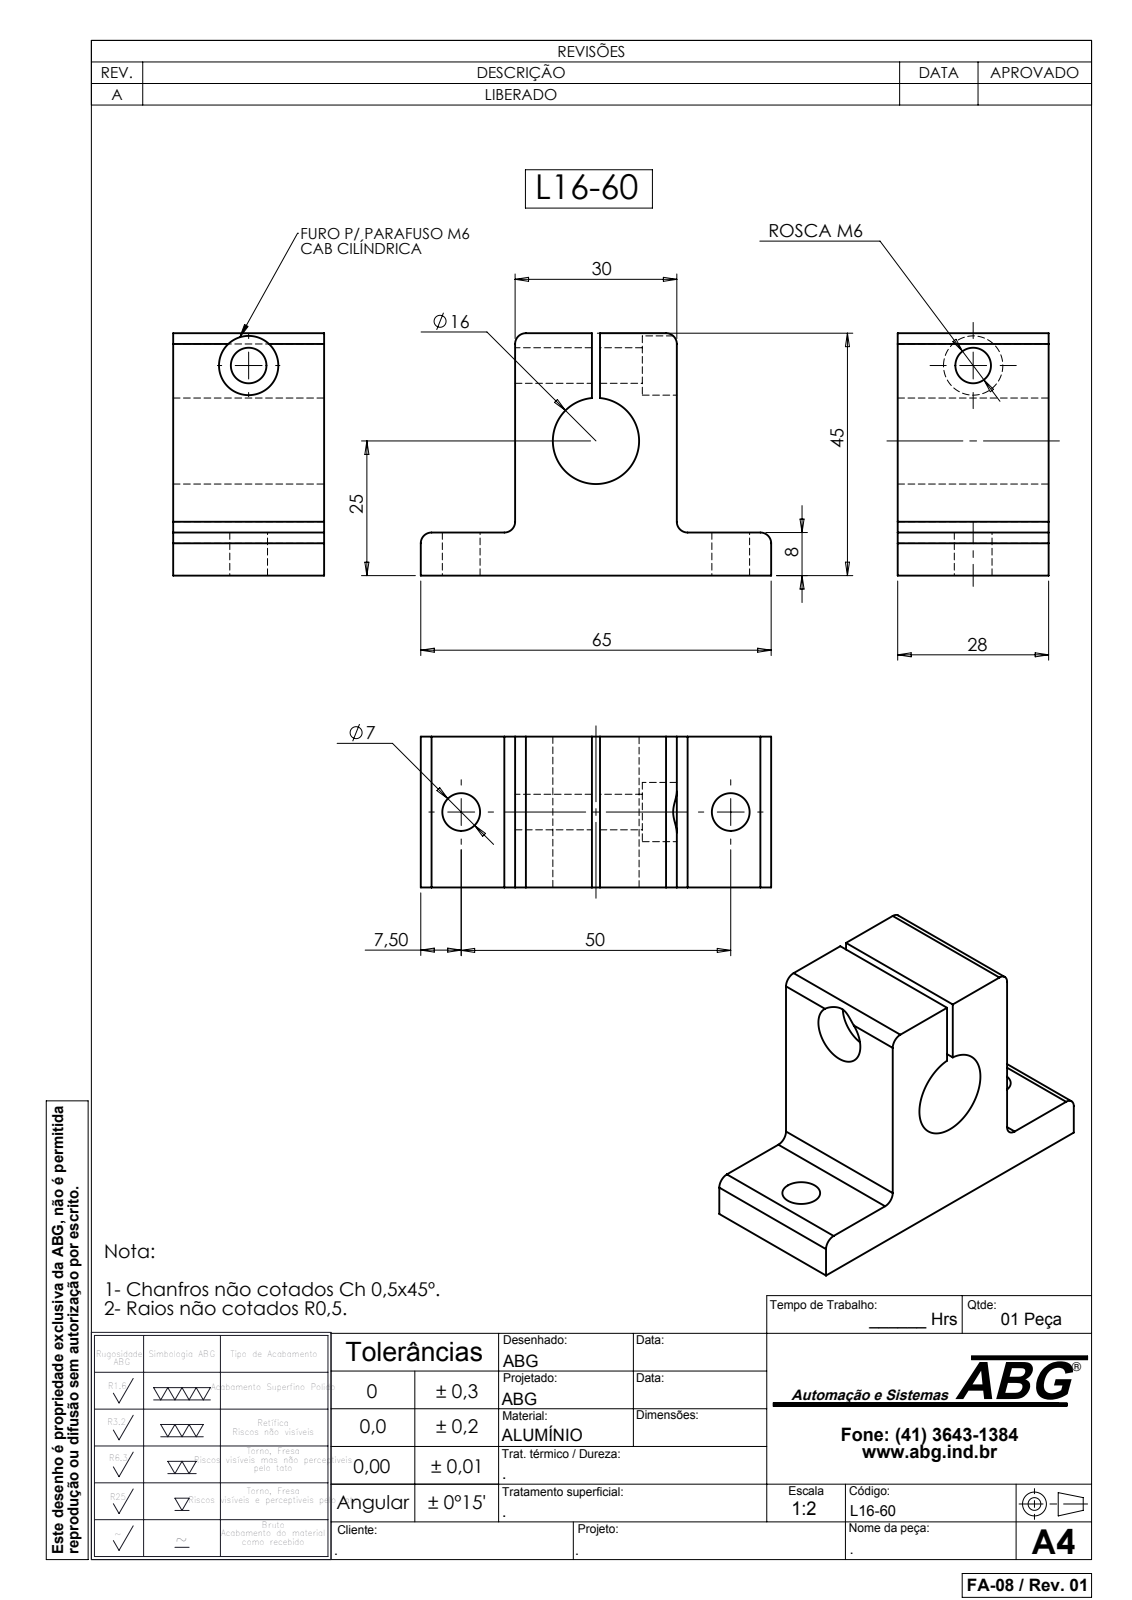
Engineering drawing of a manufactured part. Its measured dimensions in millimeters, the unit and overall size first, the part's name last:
Units: millimetres
Overall size (bounding box): 65 × 45 × 28
Round holes (diameter × count): ⌀7 ×2, ⌀6.6 ×1, ⌀11 ×1, ⌀16 ×1
Partial cylindrical surfaces — rounded edges, fillets, slot ends (radius × count): R2 ×6
Main face-to-face distances: 28, 30, 45, 8, 37, 14.25, 15.75, 17.5, 31.75, 33.25
Hole centre spacings: 50
Volume: 37 479 mm³ · Surface area: 11 569 mm²
Bodies: 1 solid, 33 faces (14 planar, 19 cylindrical, 0 other)
Part name (STEP PRODUCT): L16-60
STEP written by: SolidWorks 2007 (CONFIG_CONTROL_DESIGN)
